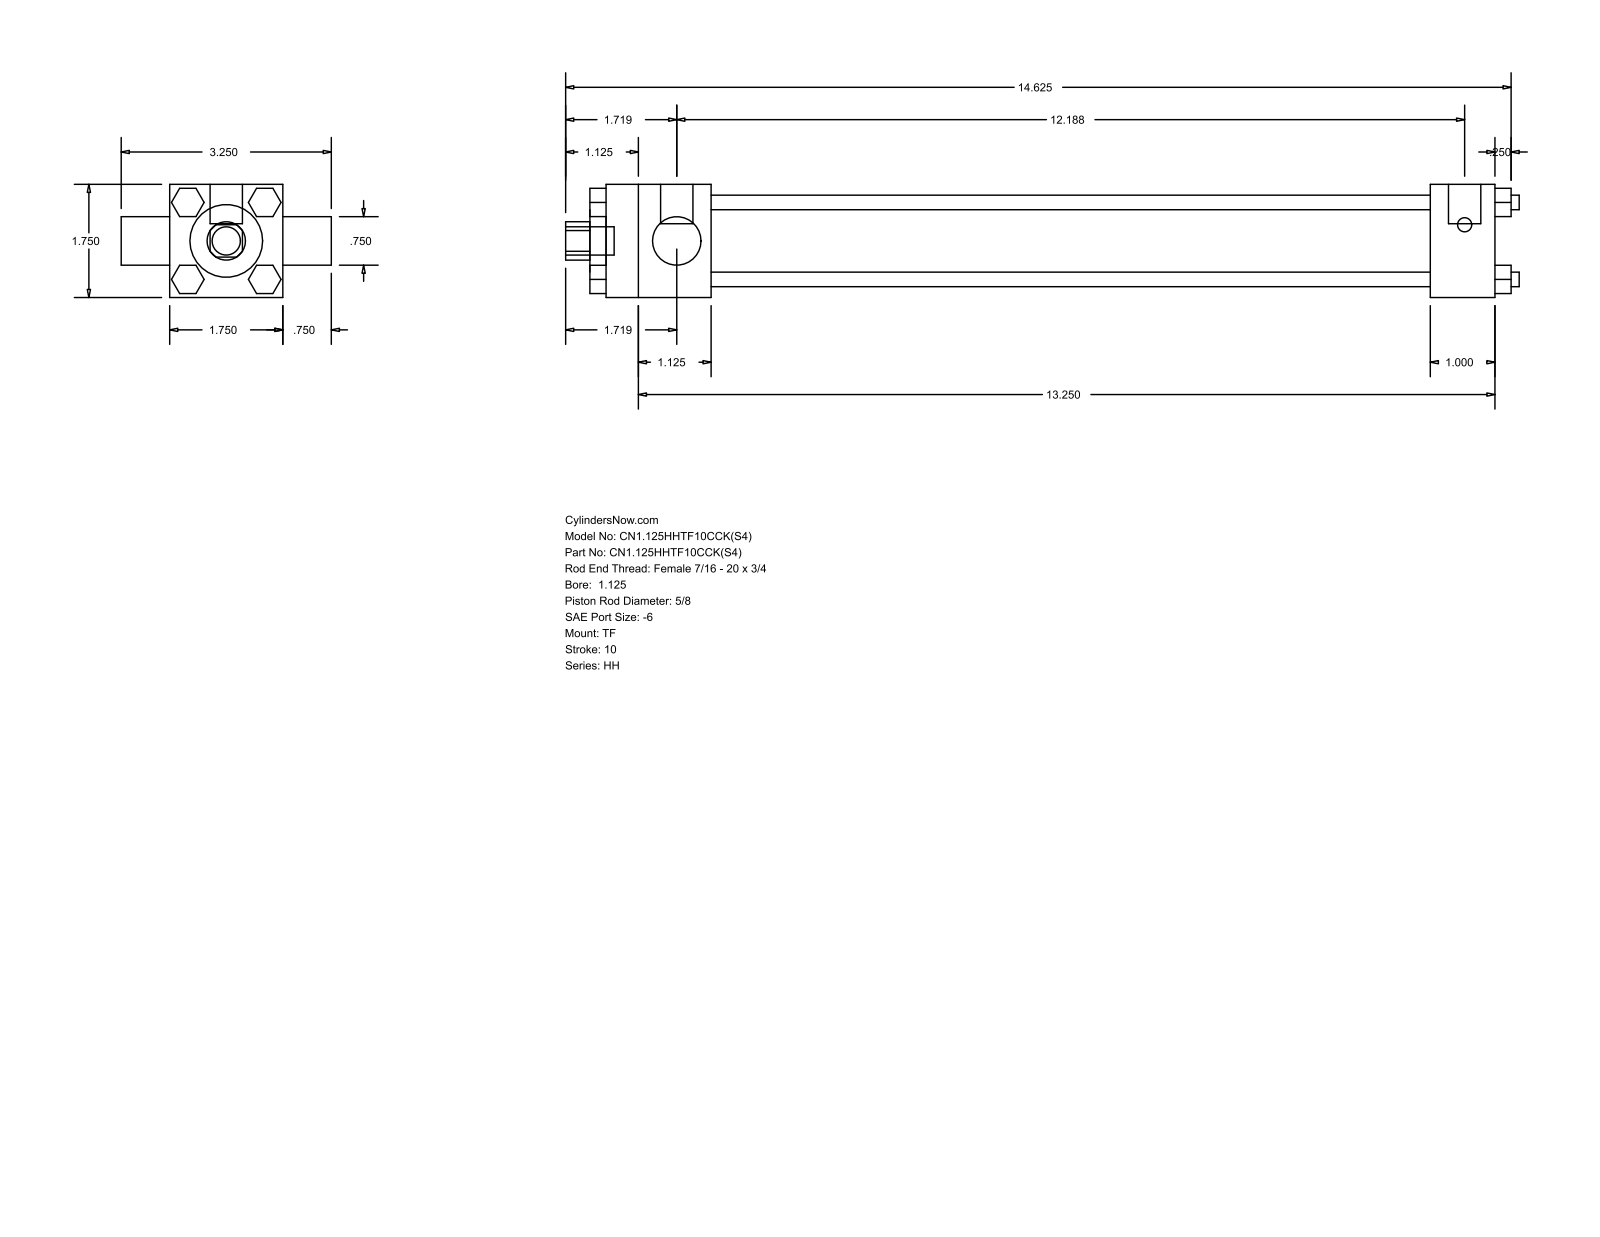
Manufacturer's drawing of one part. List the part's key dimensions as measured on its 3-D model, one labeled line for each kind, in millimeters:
Part name (STEP PRODUCT): HH_TF__0112_0.625
STEP written by: GSSL Pune (CONFIG_CONTROL_DESIGN)
Units: millimetres
Bodies: 0 solids, 120 faces (92 planar, 28 cylindrical, 0 other)
Overall size (bounding box): 374.65 × 82.55 × 44.45
Round holes (diameter × count): ⌀15.88 ×1, ⌀19.05 ×1, ⌀28.57 ×1, ⌀34.92 ×1
Round bosses / shafts (diameter × count): ⌀5.71 ×4, ⌀5.56 ×3, ⌀12.7 ×2, ⌀11.11 ×1
Partial cylindrical surfaces — rounded edges, fillets, slot ends (radius × count): R7.54 ×1
Main face-to-face distances: 44.46, 11.11, 282.58, 307.97, 25.39, 41.27, 323.85, 349.24, 47.62, 6.35
